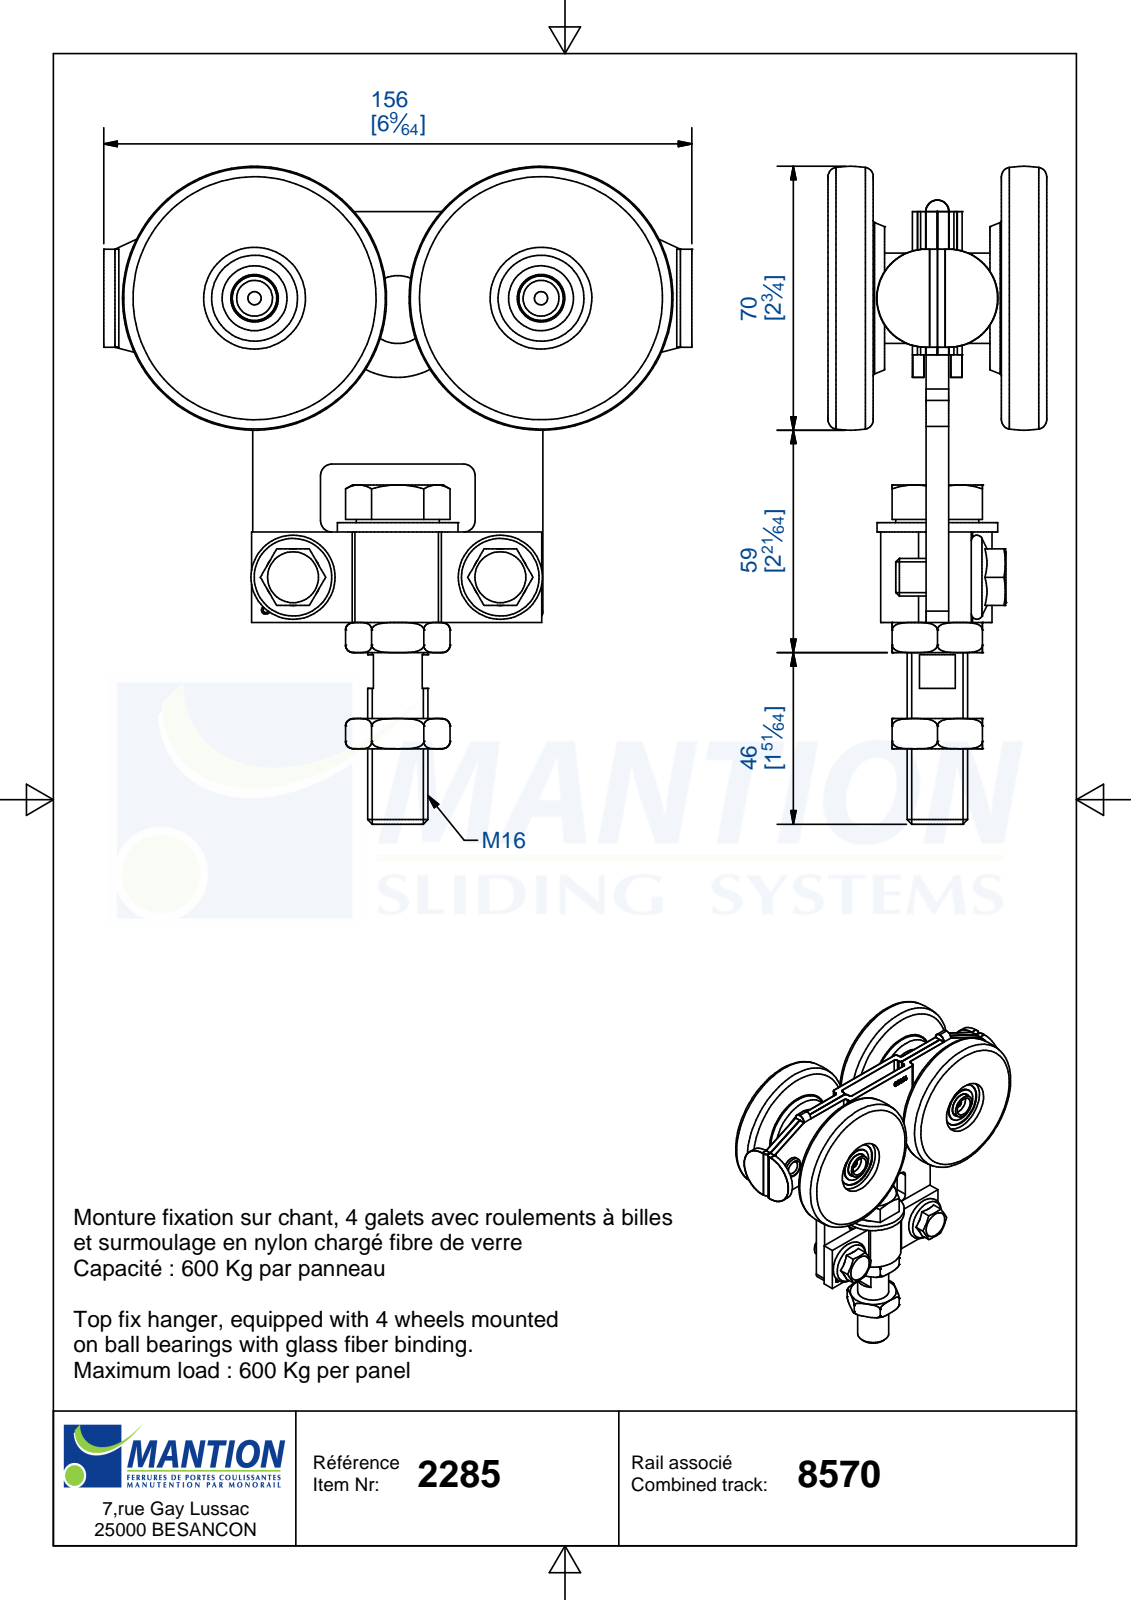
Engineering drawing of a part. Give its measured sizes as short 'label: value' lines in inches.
name: Pièce2
written by: Autodesk Inventor 2017 (AUTOMOTIVE_DESIGN)
unit: in
bodies: 4 solids, 627 faces (296 planar, 163 cylindrical, 168 other)
size: 6.87 × 6.142 × 2.205
volume: 19.37 in³; area: 159.6 in²
holes: 2× ⌀0.138, 2× ⌀0.205, 2× ⌀0.374, 2× ⌀0.398, 2× ⌀0.472, 2× ⌀0.48, 2× ⌀0.904, 2× ⌀1.063, 1× ⌀0.638, 1× ⌀0.669
bosses: 2× ⌀0.945, 2× ⌀0.71, 2× ⌀0.465, 2× ⌀0.409, 2× ⌀0.354, 1× ⌀1.26, 1× ⌀0.866, 1× ⌀0.709
rounds: 40× R0.051, 12× R0.118, 6× R0.039, 6× R0.079, 2× R0.098, 2× R0.12, 2× R0.512, 2× R0.787
face distances: 0.472, 0.984, 0.748, 0.512, 1.732, 1.22, 2.205, 0.98, 1.224, 0.508
hole spacings: 0.984, 1.501, 2.483, 3.976, 2.165, 2.941, 2.944, 2.992
